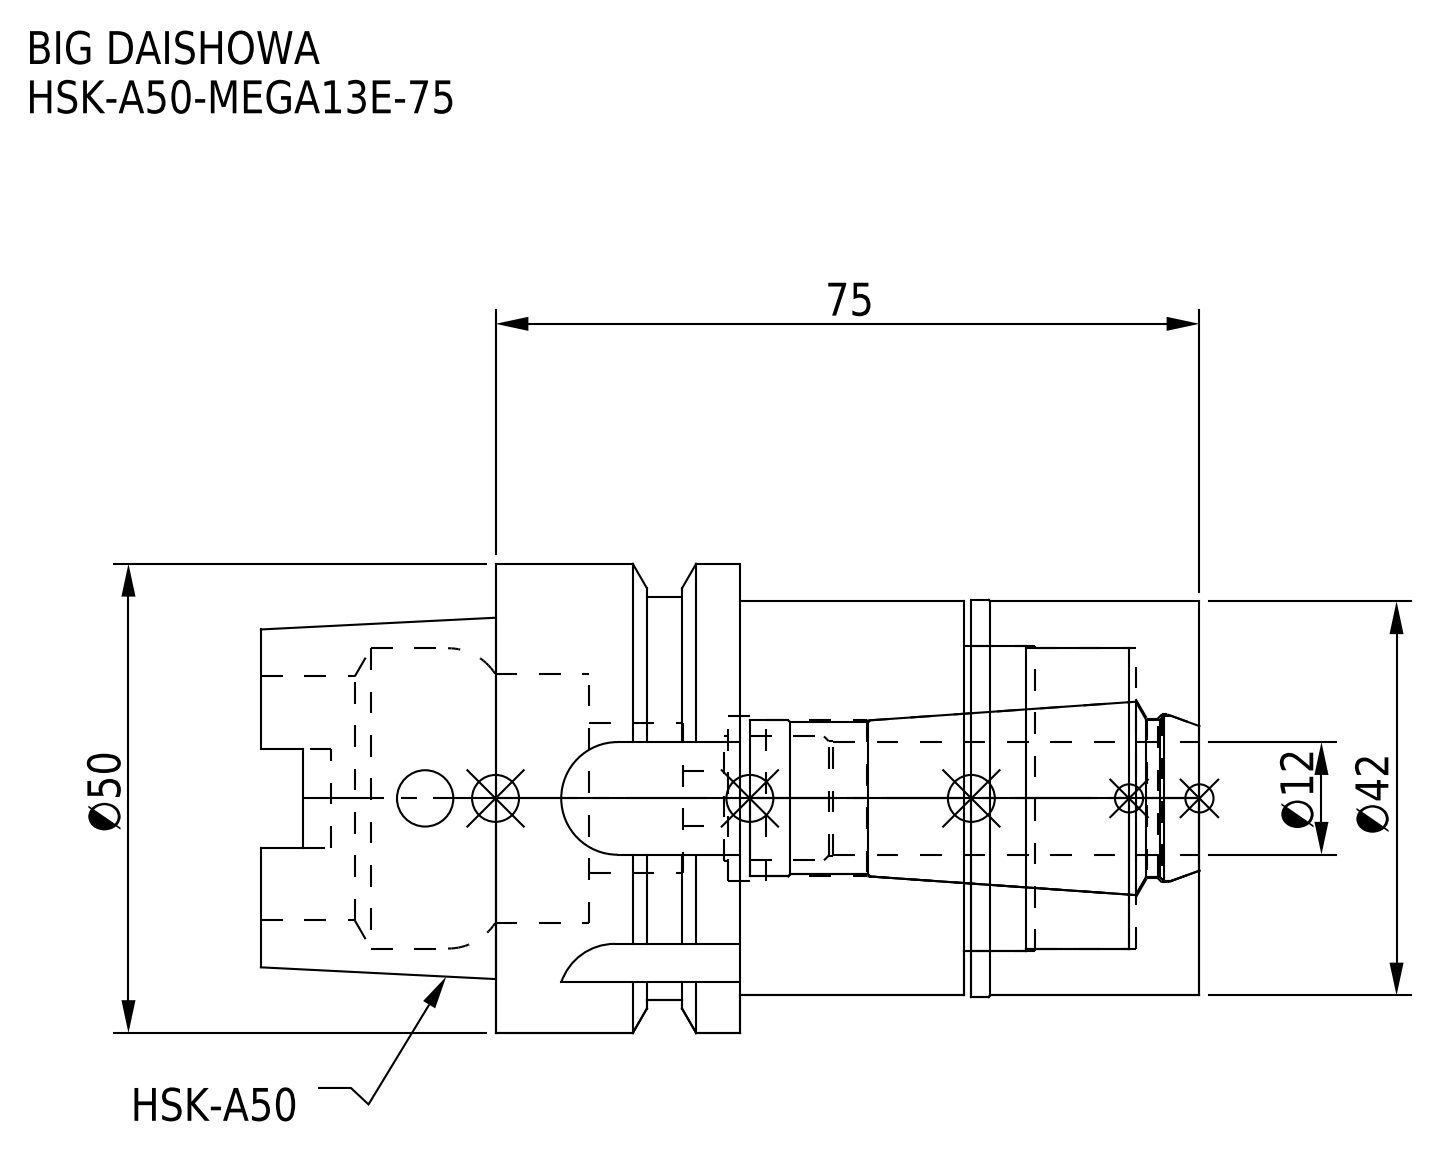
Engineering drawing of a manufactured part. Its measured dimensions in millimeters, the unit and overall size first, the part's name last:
Units: millimetres
Overall size (bounding box): 100 × 50 × 50
Round holes (diameter × count): ⌀5.8 ×1, ⌀6 ×1, ⌀13.3 ×1, ⌀16 ×1, ⌀16.6 ×1, ⌀17 ×1, ⌀17.53 ×1, ⌀17.9 ×1, ⌀26 ×1, ⌀26.6 ×1, ⌀32 ×1, ⌀32.5 ×1
Round bosses / shafts (diameter × count): ⌀50 ×1, ⌀43 ×1, ⌀42.3 ×1, ⌀42 ×1
Partial cylindrical surfaces — rounded edges, fillets, slot ends (radius × count): R2.38 ×4, R6 ×4
Main face-to-face distances: 75, 24.3, 50.7, 25.1, 0.8, 49.9, 17.5, 7.5, 68.2, 6.8
Volume: 103 457 mm³ · Surface area: 30 117 mm²
Bodies: 2 solids, 125 faces (46 planar, 55 cylindrical, 24 other)
Part name (STEP PRODUCT): MEN13_1.stp; HSK-A50-MEGA13E-75-120.stp; HSK-A50-MEGA13E-75-120-FreeParts; HSK-A50-MEGA13E-75 (+3 more)
STEP written by: SolidWorks 2019 (CONFIG_CONTROL_DESIGN)
